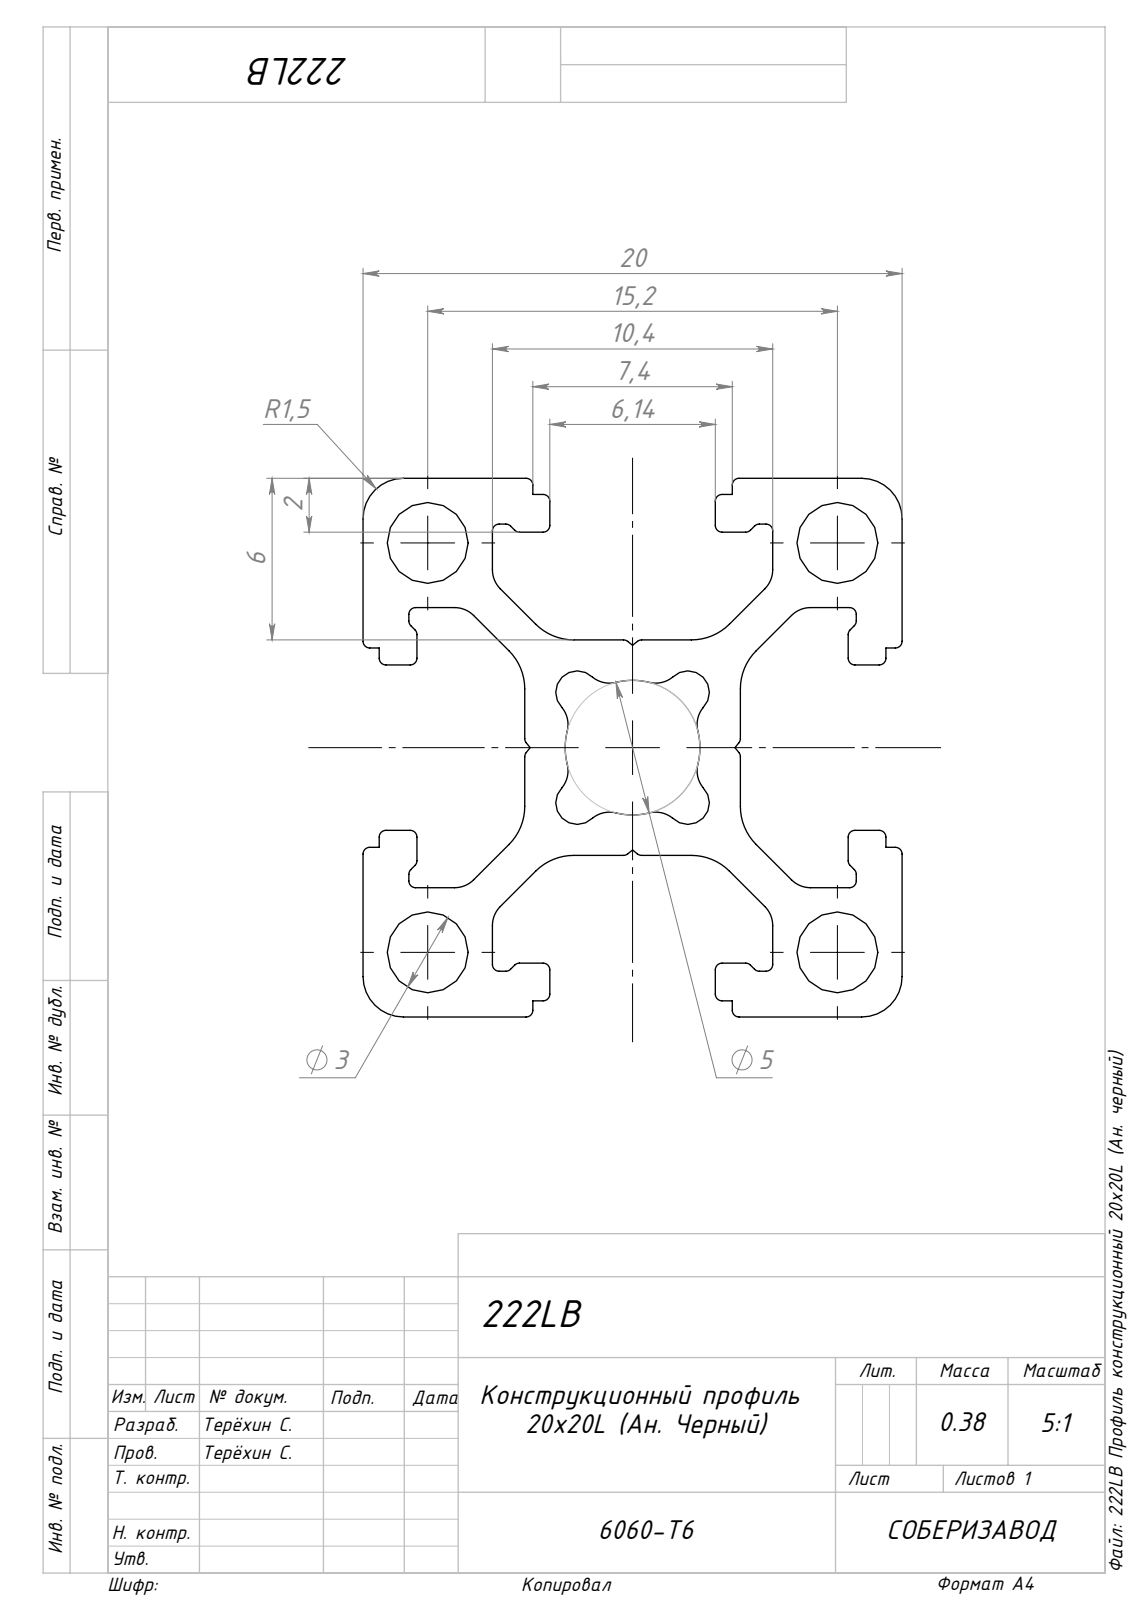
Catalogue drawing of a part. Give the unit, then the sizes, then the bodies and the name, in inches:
Units: inches
Overall size (bounding box): 16.752 × 0.787 × 0.787
Round holes (diameter × count): ⌀0.118 ×4
Partial cylindrical surfaces — rounded edges, fillets, slot ends (radius × count): R0.01 ×56, R0.039 ×16, R0.079 ×8, R0.031 ×4, R0.059 ×4, R0.098 ×1
Main face-to-face distances: 0.787, 0.551, 0.236, 0.189, 0.598, 0.047, 0.362, 0.055, 0.472, 0.315
Hole centre spacings: 0.598, 0.846
Volume: 3.69 in³ · Surface area: 138 in²
Bodies: 1 solid, 195 faces (90 planar, 105 cylindrical, 0 other)
Part name (STEP PRODUCT): 222LB Профиль конструкционный 20х20L (Ан. черный)
STEP written by: SolidWorks 2025 (AUTOMOTIVE_DESIGN)
